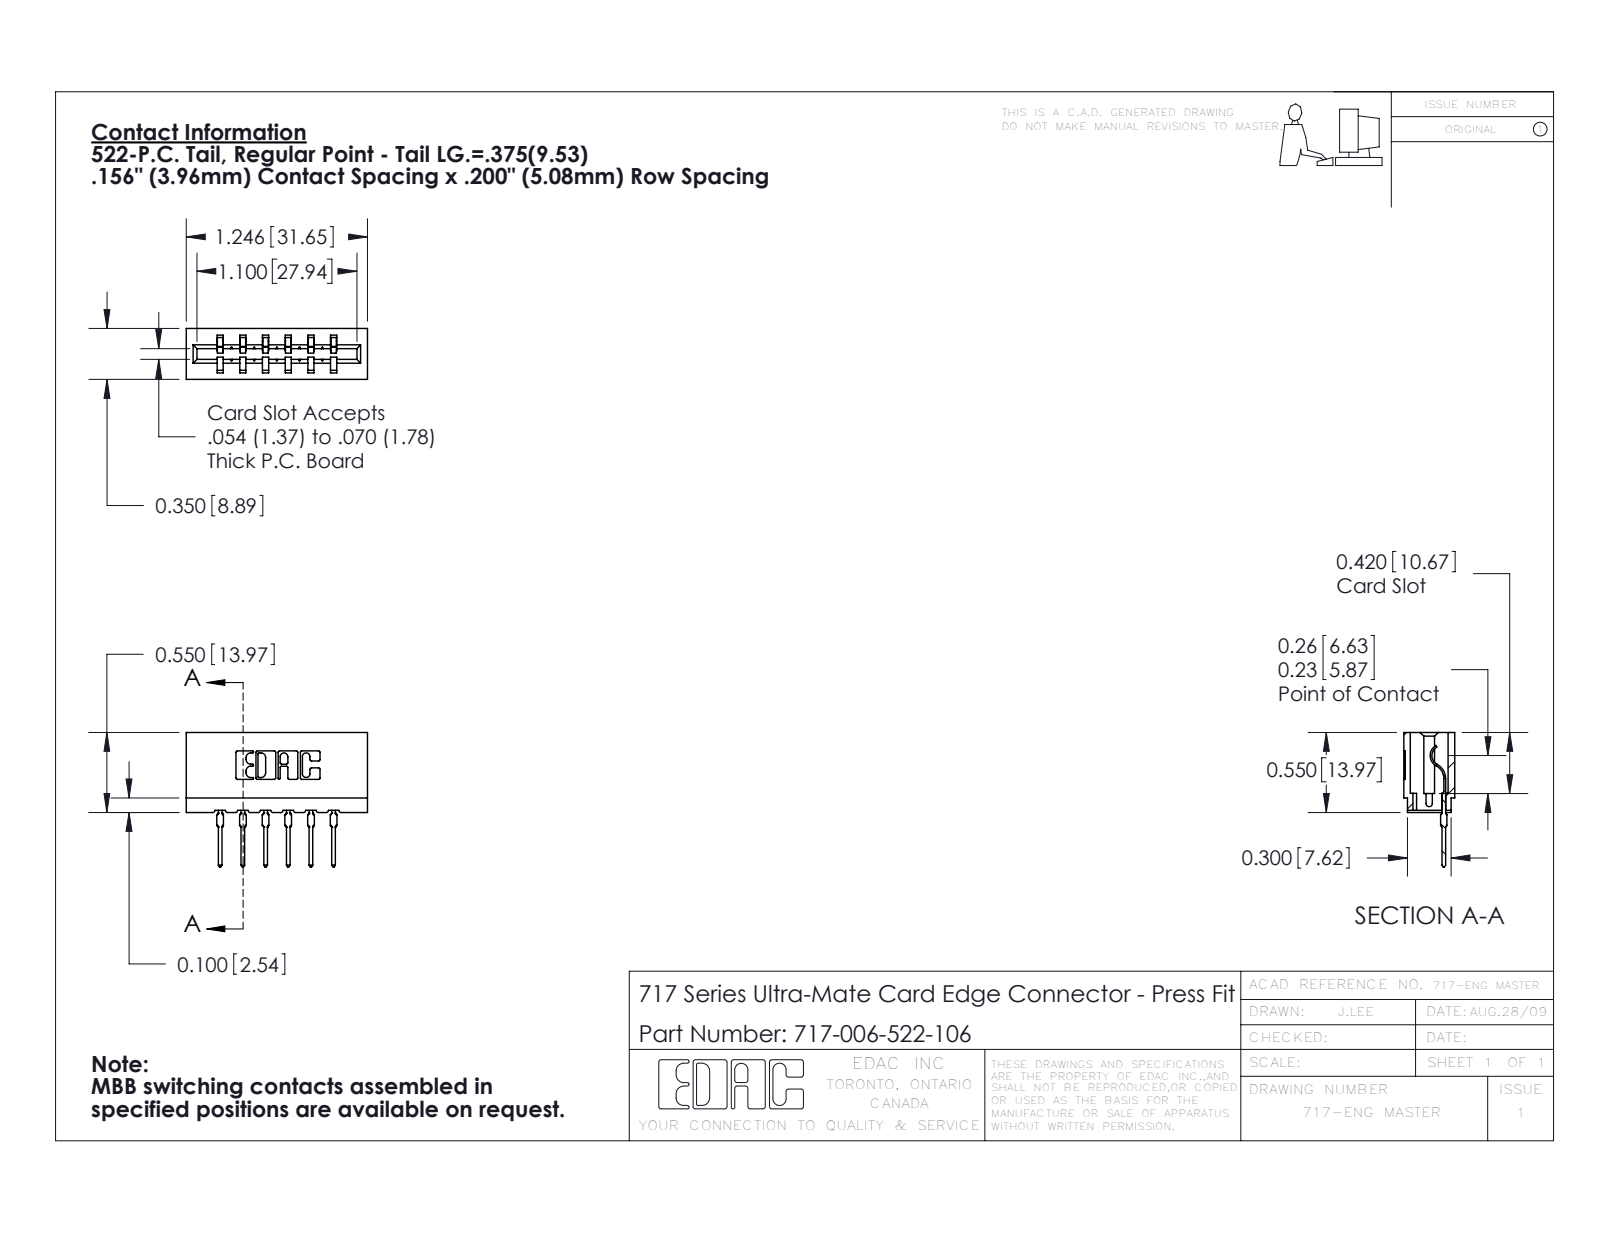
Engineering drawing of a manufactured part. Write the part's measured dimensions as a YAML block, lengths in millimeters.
part_name: "717-006-522-106; 745-292-001_522; 717 Part_Insulator Option - 06"
step_written_by: "SolidWorks 2016 (CONFIG_CONTROL_DESIGN)"
units: millimeters
bodies: {solids: 7, faces: 772, planar: 462, cylindrical: 154, other: 156}
overall_size: [31.6, 23.5, 8.9]
volume: 2830
surface_area: 3609
partial_cylinders:
  - {radius: 0.3, count: 22}
  - {radius: 0.4, count: 12}
  - {radius: 0.5, count: 12}
  - {radius: 0.2, count: 6}
  - {radius: 0.8, count: 6}
  - {radius: 0.1, count: 4}
  - {radius: 0.3, count: 4}
  - {radius: 0.7, count: 3}
face_to_face_distances: [5.4, 4, 3.5, 8.9, 5, 7.9, 15.8, 1.1, 7.9, 11.9]
